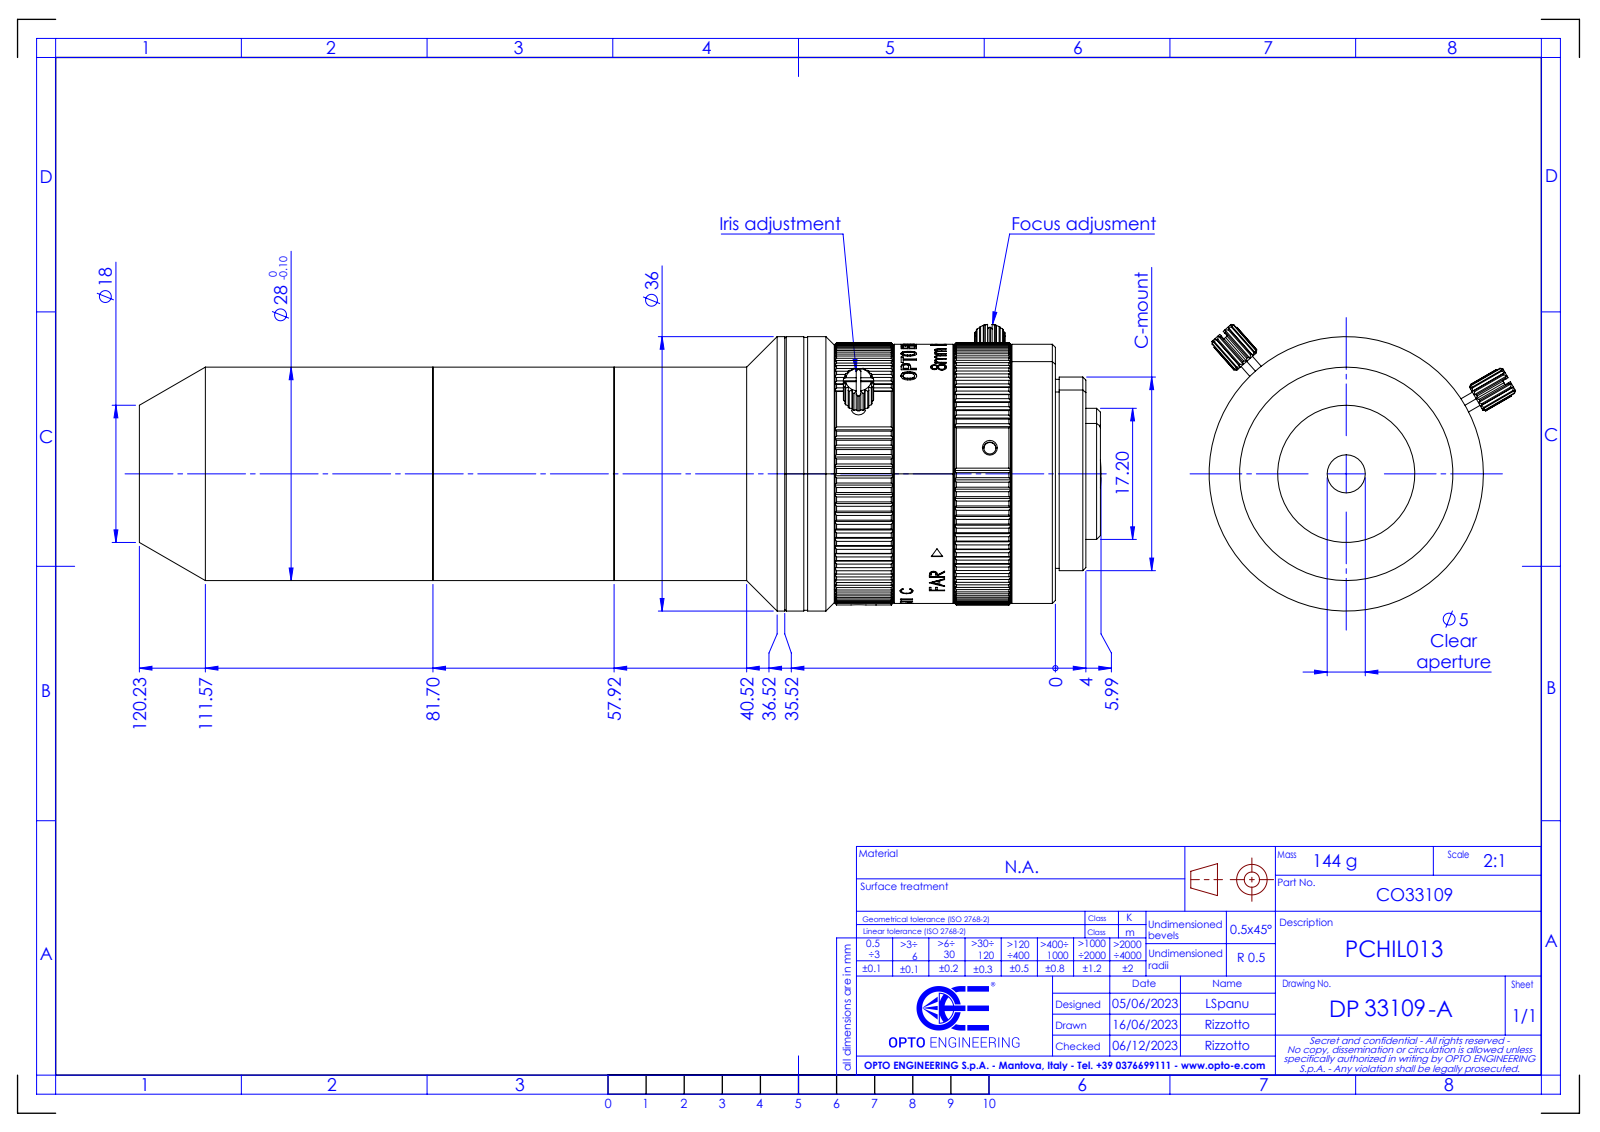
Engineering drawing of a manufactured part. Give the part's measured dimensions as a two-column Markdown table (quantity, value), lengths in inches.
| quantity | value |
| --- | --- |
| part name | DP33109-A_PCHIL013 |
| STEP written by | SolidWorks 2021 (CONFIG_CONTROL_DESIGN) |
| units | inches |
| bodies | 0 solids, 1315 faces (559 planar, 309 cylindrical, 447 other) |
| overall size | 4.969 × 1.584 × 1.481 |
| round holes (diameter × count) | 0.063 × 4, 0.106 × 3, 0.031 × 2, 0.197 × 1, 0.52 × 1, 0.59 × 1, 0.843 × 1, 1.32 × 1 |
| round bosses / shafts (diameter × count) | 0.079 × 2, 1.417 × 1, 1.409 × 1, 1.354 × 1, 1.339 × 1, 1.102 × 1, 1 × 1, 0.976 × 1 |
| partial cylindrical surfaces (radius × count) | 0.079 × 2, 0.665 × 1 |
| main face-to-face distances | 1.083, 1.105, 0.022, 3.628, 4.712, 4.733, 1.517, 2.111, 3.195, 3.217 |
| hole center spacings | 0.307, 0.557, 0.965, 0.259, 0.431, 0.535, 0.557, 0.615 |
